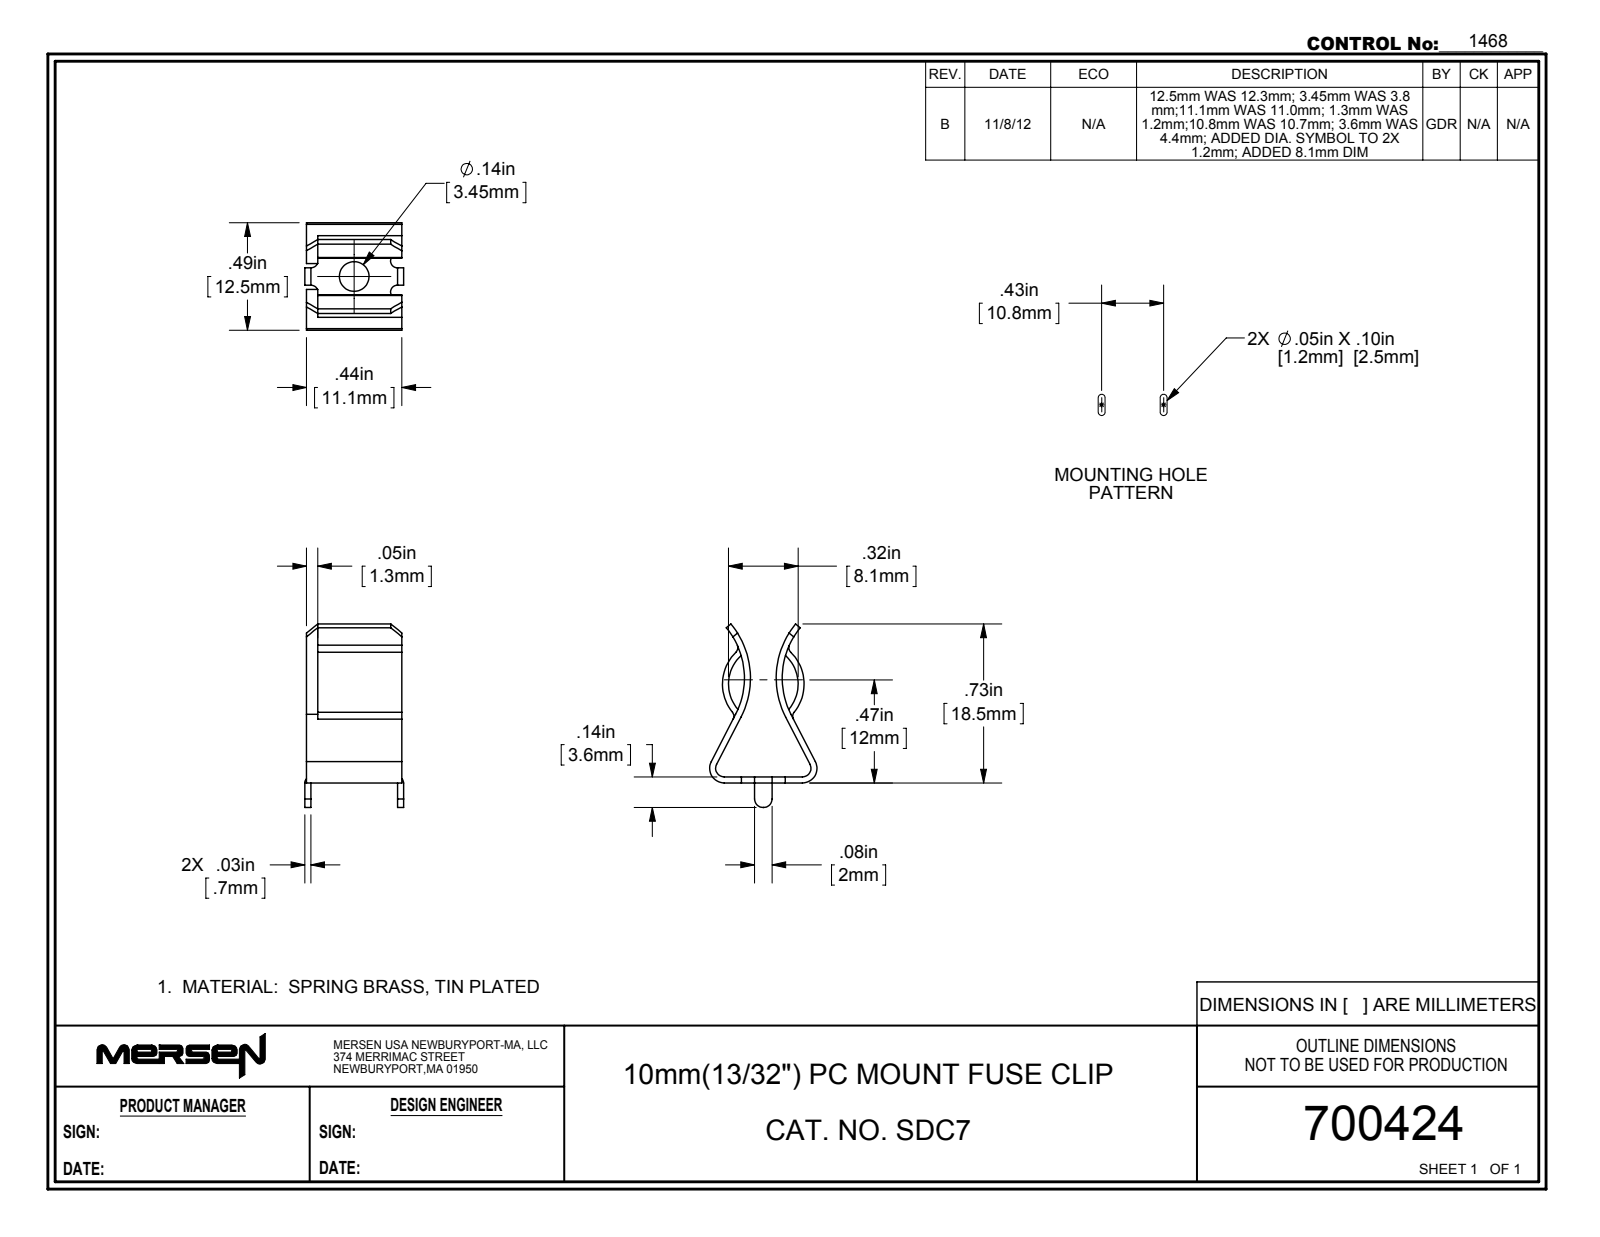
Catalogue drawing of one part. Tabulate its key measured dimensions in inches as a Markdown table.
| quantity | value |
| --- | --- |
| part name | 370015 |
| STEP written by | SolidWorks 2016 (AUTOMOTIVE_DESIGN) |
| units | inches |
| bodies | 1 solid, 82 faces (34 planar, 48 cylindrical, 0 other) |
| overall size | 0.869 × 0.492 × 0.453 |
| volume | 0.024 in³ |
| surface area | 1.908 in² |
| round holes (diameter × count) | 0.136 × 1 |
| partial cylindrical surfaces (radius × count) | 0.029 × 4, 0.03 × 4, 0.031 × 4, 0.039 × 4, 0.362 × 4, 0.028 × 2, 0.067 × 2, 0.177 × 2 |
| main face-to-face distances | 0.028, 0.437, 0.386, 0.051, 0.445, 0.02, 0.417, 0.425, 0.059, 0.031 |
